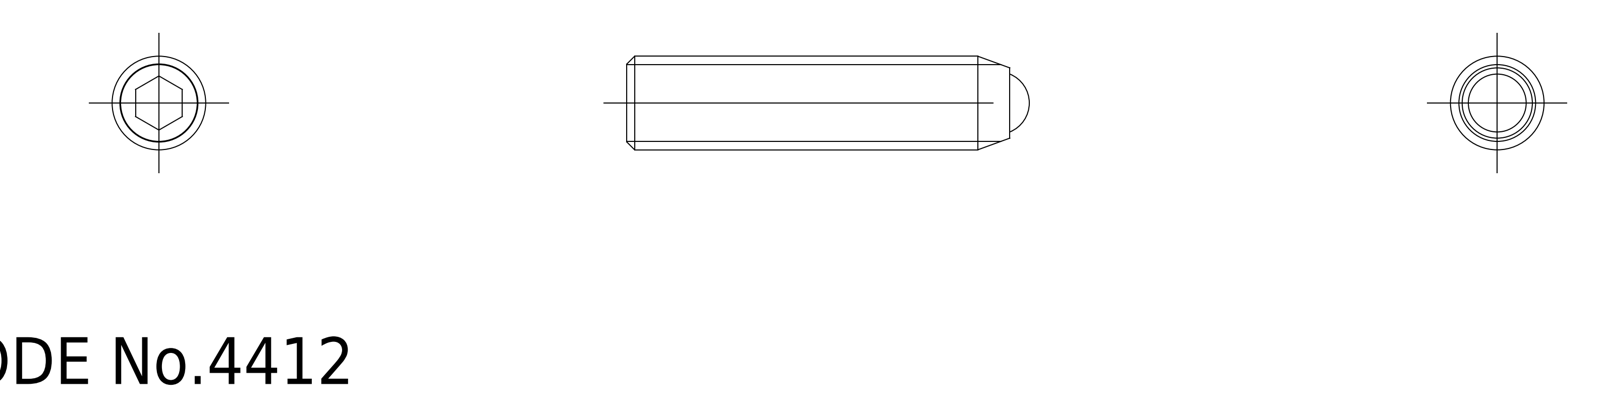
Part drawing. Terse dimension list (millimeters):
name: ball; SCSS_M6_25_R_19125_36
written by: CADfix (AUTOMOTIVE_DESIGN)
unit: mm
bodies: 2 solids, 20 faces (0 planar, 0 cylindrical, 20 other)
size: 25.8 × 6 × 6
volume: 628 mm³; area: 646 mm²
